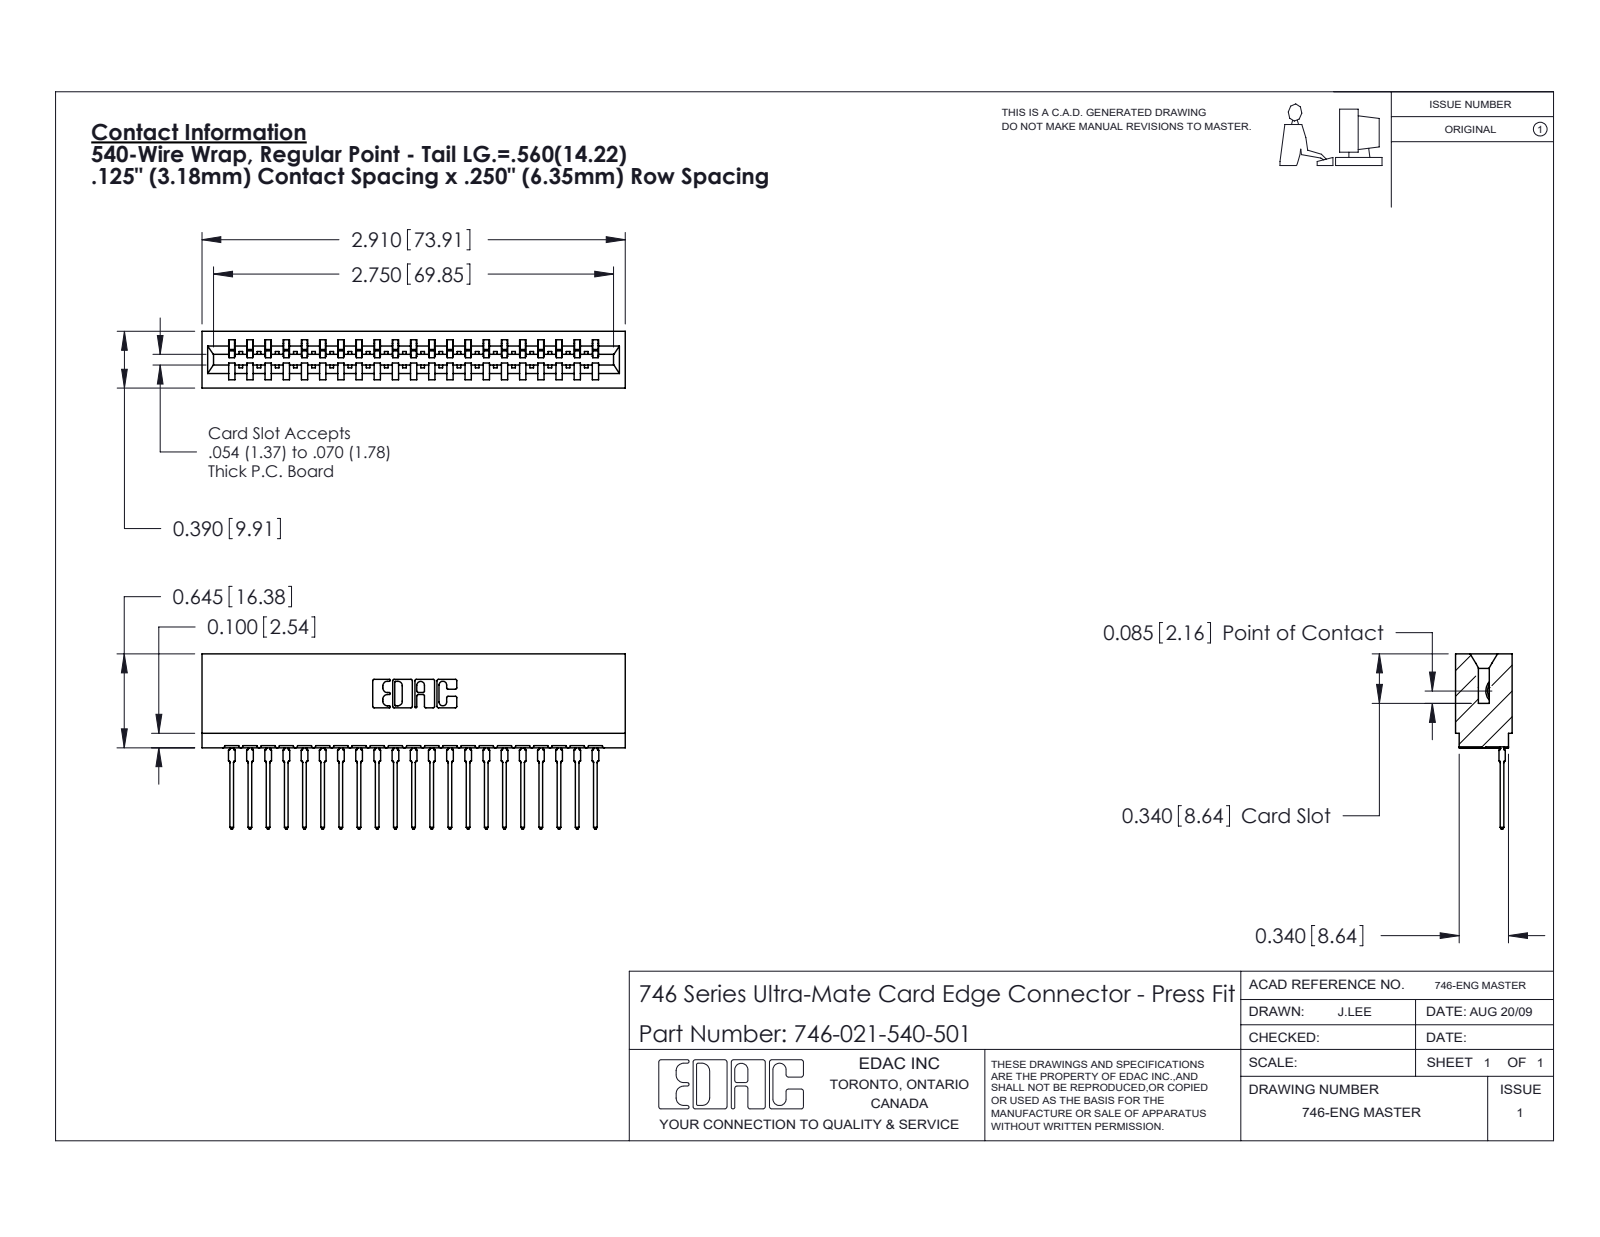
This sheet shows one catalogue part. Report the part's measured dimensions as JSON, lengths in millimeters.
{"part_name": "746-021-540-501; 746 Part_.340 Slot Depth - 01; 746-292-001_540", "step_written_by": "SolidWorks 2020 (CONFIG_CONTROL_DESIGN)", "units": "millimeters", "bodies": {"solids": 22, "faces": 2365, "planar": 1378, "cylindrical": 441, "other": 546}, "overall_size": [73.9, 30.6, 9.9], "volume_mm3": 8470, "surface_area_mm2": 11370, "partial_cylinders_radius": [[0.5, 42], [0.3, 22], [0.4, 22], [0.2, 6], [0.8, 6], [0.1, 4], [0.3, 4], [0.7, 3]], "face_to_face_distances": [6.4, 1.4, 8.5, 9.9, 12.7, 0.6, 7.8, 3.2, 7.4, 3.2]}
